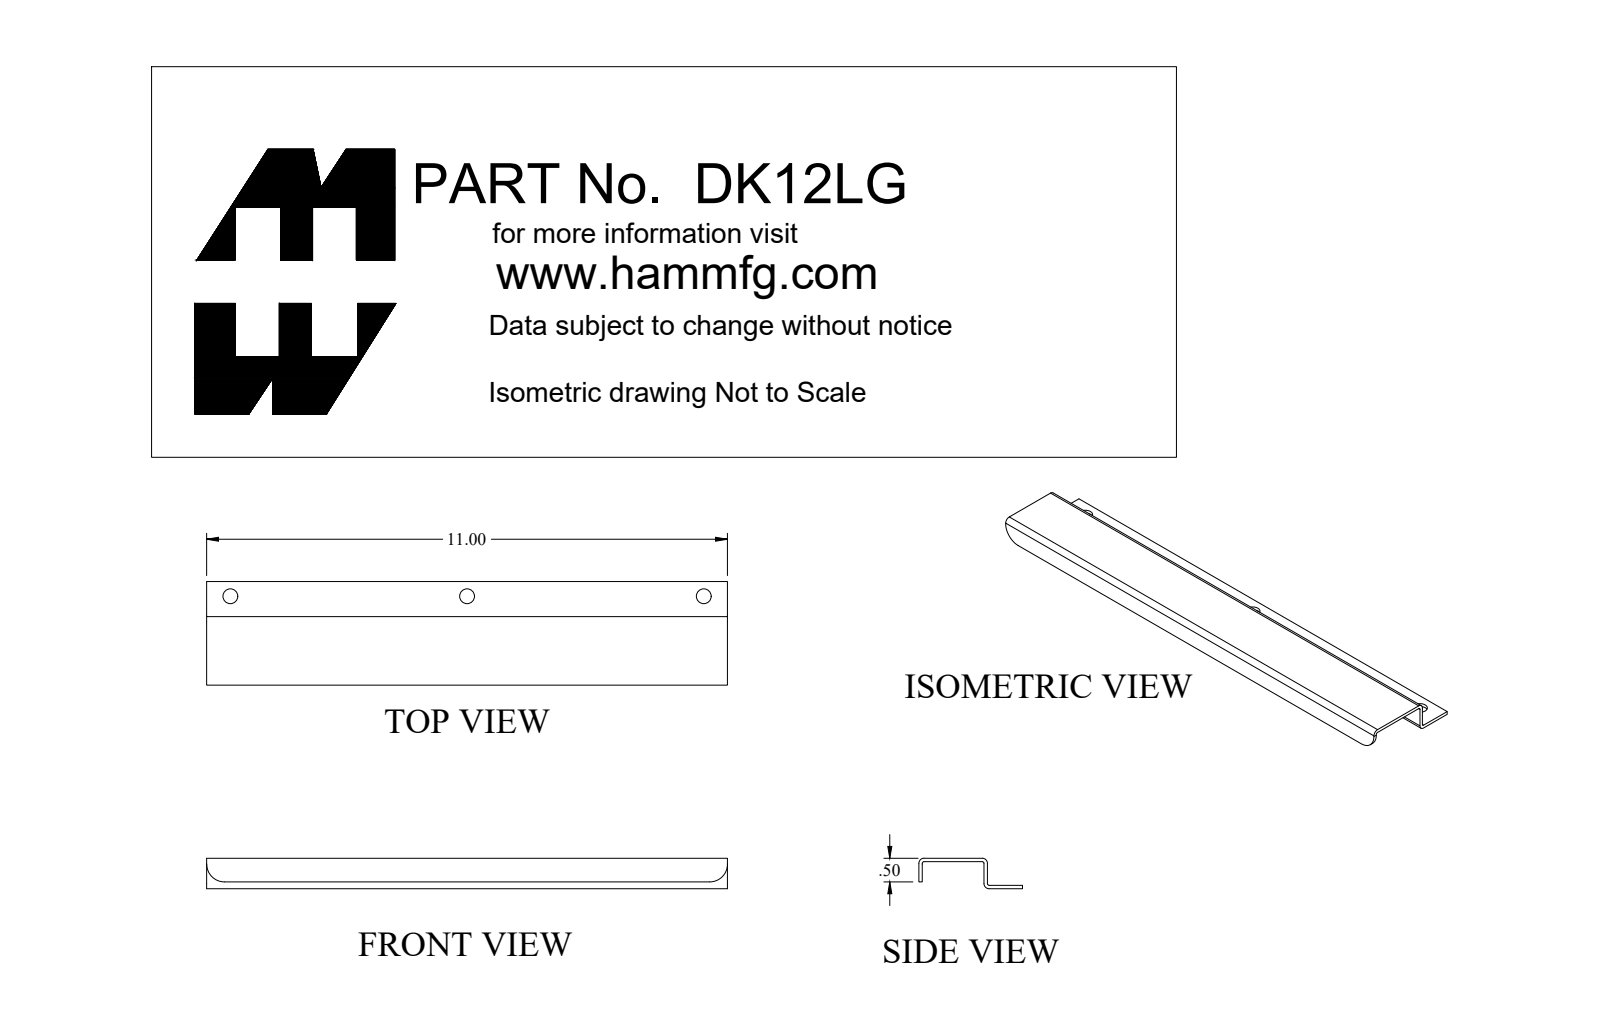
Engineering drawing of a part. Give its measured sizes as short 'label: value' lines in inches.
name: DK12LG_Default
written by: SolidWorks 2018 (CONFIG_CONTROL_DESIGN)
unit: in
bodies: 5 solids, 65 faces (35 planar, 24 cylindrical, 6 other)
size: 11 × 2.188 × 1.322
volume: 3.062 in³; area: 90.38 in²
holes: 3× ⌀0.313, 1× ⌀0.201, 1× ⌀0.275
bosses: 1× ⌀0.625, 1× ⌀0.483, 1× ⌀0.25
rounds: 3× R0.036, 3× R0.108, 2× R0.375
face distances: 0.072, 0.572, 0.644, 1.376, 0.5, 0.063, 0.635, 0.707, 0.135, 1.448
hole spacings: 5, 10
